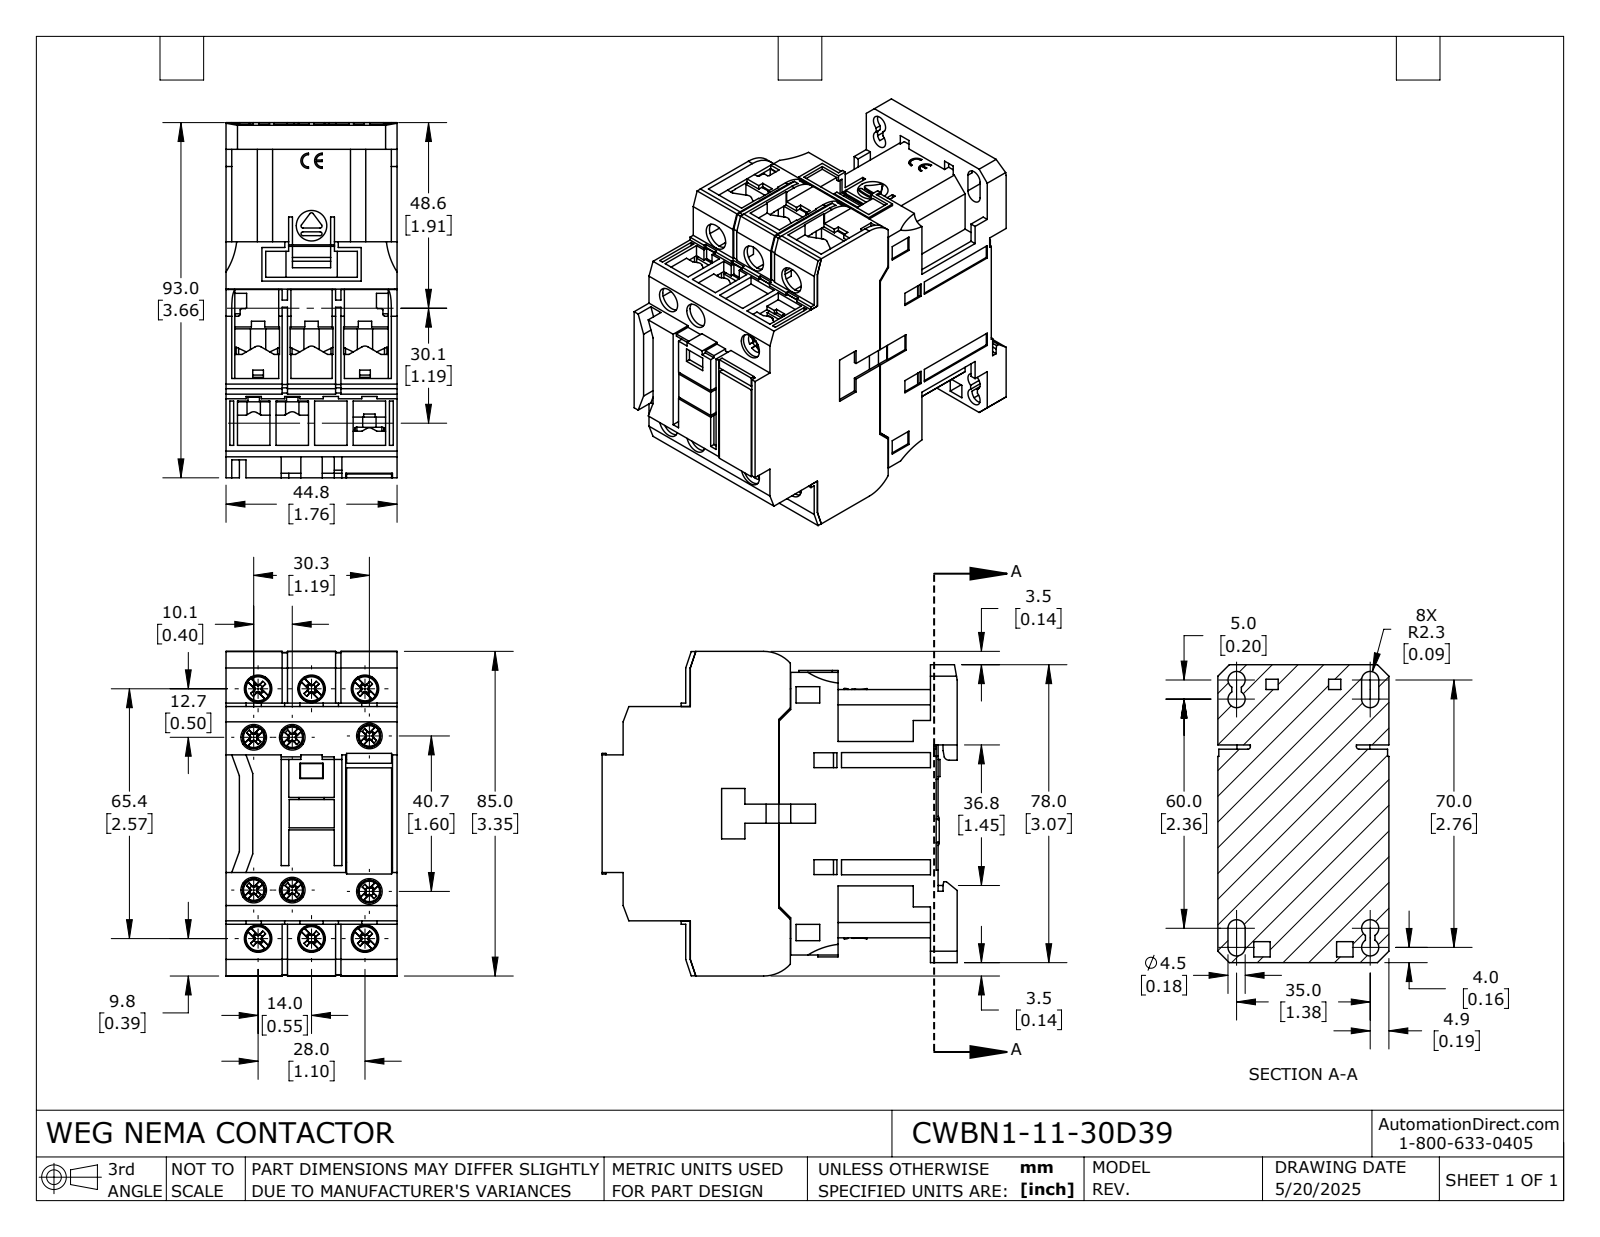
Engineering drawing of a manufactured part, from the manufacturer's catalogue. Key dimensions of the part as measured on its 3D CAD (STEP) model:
Part name (STEP PRODUCT): CWBN1-11-30D39
STEP written by: SolidWorks 2024 (AUTOMOTIVE_DESIGN)
Units: inches
Bodies: 42 solids, 2540 faces (1924 planar, 437 cylindrical, 179 other)
Overall size (bounding box): 3.661 × 3.346 × 1.764
Volume: 14.55 in³ · Surface area: 115.4 in²
Round holes (diameter × count): ⌀0.124 ×6, ⌀0.142 ×6, ⌀0.264 ×6, ⌀0.283 ×6, ⌀0.177 ×4
Round bosses / shafts (diameter × count): ⌀0.201 ×6, ⌀0.169 ×6, ⌀0.157 ×6, ⌀0.138 ×6, ⌀0.107 ×6
Partial cylindrical surfaces — rounded edges, fillets, slot ends (radius × count): R0.02 ×34, R0.028 ×24, R0.071 ×12, R0.081 ×12, R0.964 ×12, R1.079 ×12, R2.128 ×12, R3.127 ×12
Main face-to-face distances: 1.764, 0.047, 0.132, 1.754, 0.024, 1.622, 1.717, 3.445, 0.059, 0.071
Hole centre spacings: 0.551, 2.633, 2.575, 0.165, 0.174, 0.197, 0.398, 0.488
